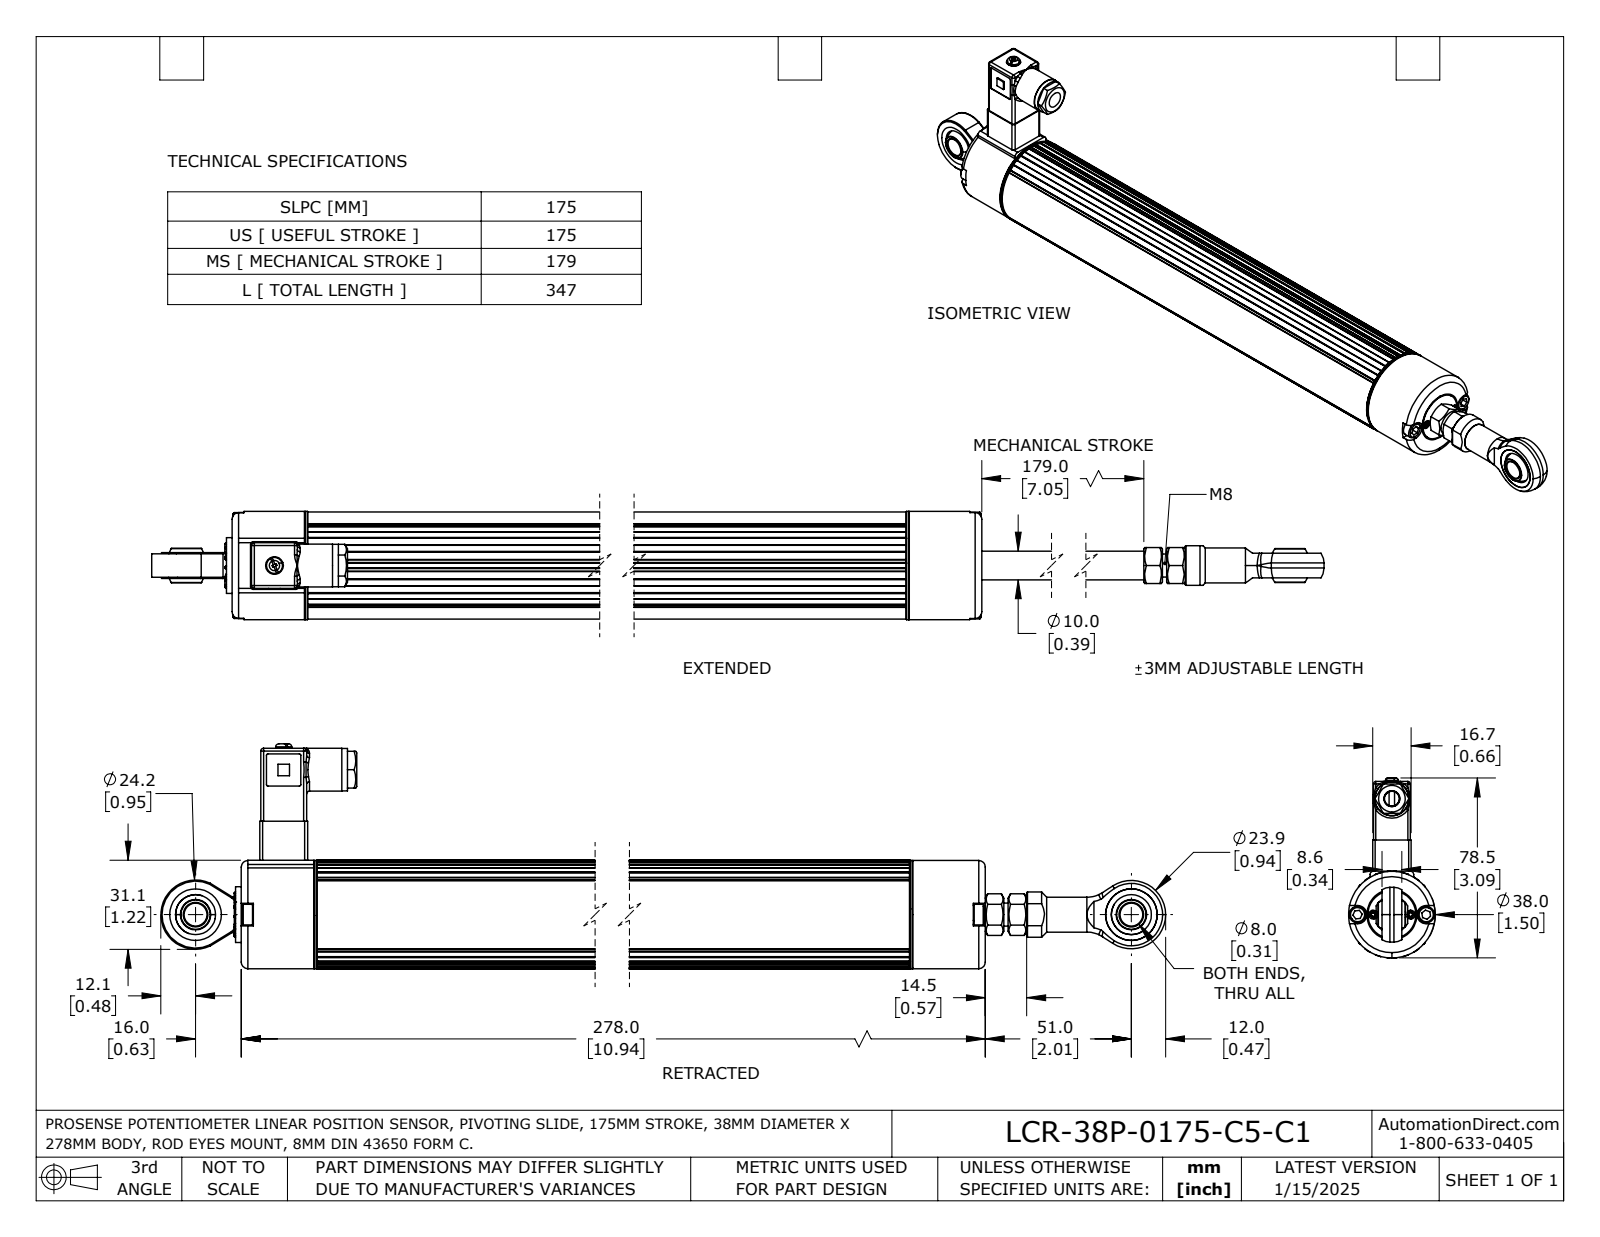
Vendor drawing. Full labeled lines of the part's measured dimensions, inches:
Part name (STEP PRODUCT): LCR-38P-0175-C5-C1
STEP written by: SolidWorks 2023 (AUTOMOTIVE_DESIGN)
Units: inches
Bodies: 11 solids, 657 faces (295 planar, 210 cylindrical, 152 other)
Overall size (bounding box): 14.53 × 3.093 × 1.488
Volume: 19.98 in³ · Surface area: 102.8 in²
Round holes (diameter × count): ⌀0.102 ×6, ⌀0.091 ×4, ⌀0.315 ×3, ⌀0.551 ×3, ⌀0.094 ×2, ⌀0.1 ×2, ⌀0.111 ×2, ⌀0.134 ×2, ⌀0.152 ×2, ⌀0.165 ×2, ⌀0.079 ×1, ⌀0.118 ×1
Round bosses / shafts (diameter × count): ⌀0.063 ×6, ⌀0.283 ×4, ⌀0.15 ×4, ⌀0.48 ×2, ⌀0.079 ×2, ⌀1.488 ×1, ⌀0.823 ×1, ⌀0.768 ×1
Partial cylindrical surfaces — rounded edges, fillets, slot ends (radius × count): R0.008 ×32, R0.039 ×20, R0.02 ×12, R0.016 ×6, R0.012 ×2, R0.059 ×2, R0.083 ×2, R0.098 ×2
Main face-to-face distances: 8.858, 1.043, 9.902, 0.031, 0.045, 0.612, 0.598, 0.014, 0.644, 0.138
Hole centre spacings: 0.632, 0.075, 0.634, 0.264, 0.268, 0.285, 0.323, 0.394
